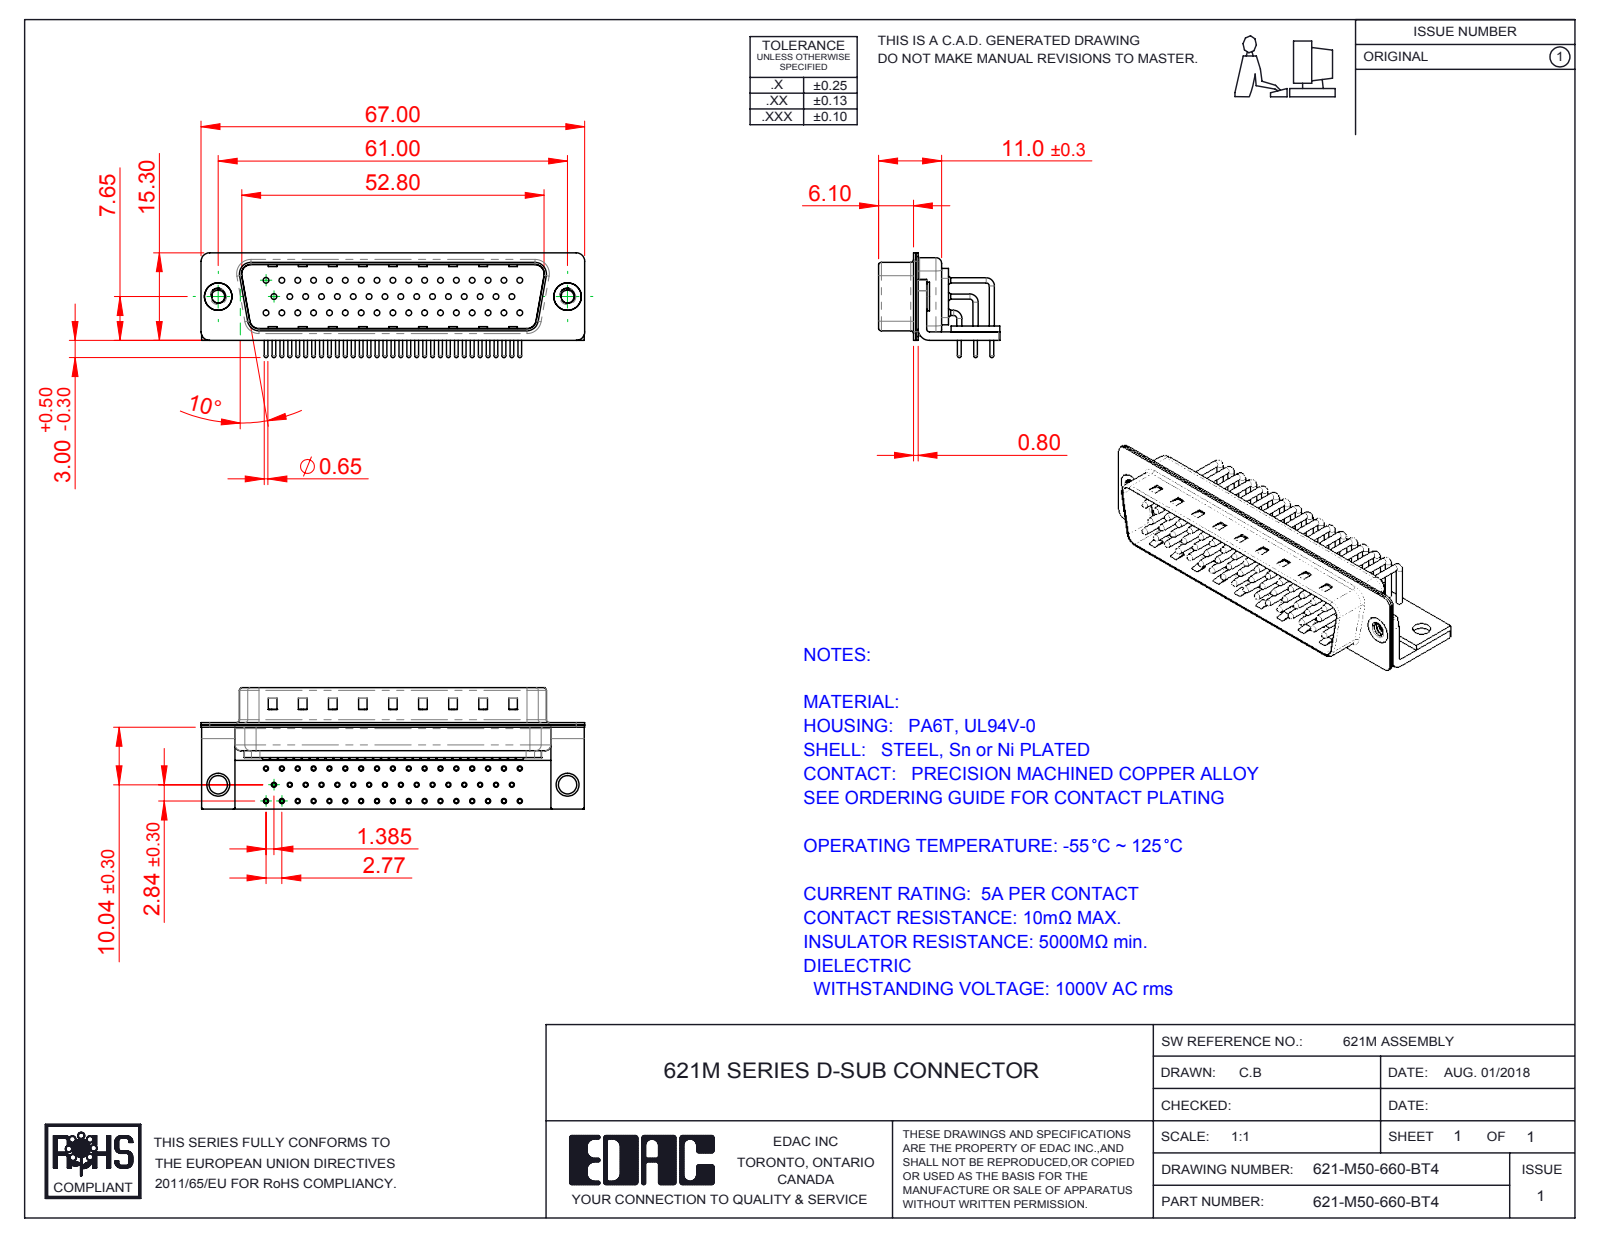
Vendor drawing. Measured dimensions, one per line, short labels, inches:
name: 621M Contact Row 3; 621M Housing_50 Contacts; 621M Stabilizer Bracket_50 Contacts; 621M Shell Front_50 Contacts (+6 more)
written by: SolidWorks 2016 (CONFIG_CONTROL_DESIGN)
unit: in
bodies: 58 solids, 6062 faces (3429 planar, 2063 cylindrical, 570 other)
size: 2.638 × 0.835 × 0.72
volume: 0.35 in³; area: 22.56 in²
holes: 50× ⌀0.035, 50× ⌀0.039, 50× ⌀0.067, 50× ⌀0.079, 2× ⌀0.089, 2× ⌀0.126, 2× ⌀0.157, 2× ⌀0.189
bosses: 58× ⌀0.035, 50× ⌀0.059, 50× ⌀0.026, 2× ⌀0.197, 2× ⌀0.193
rounds: 50× R0.04, 16× R0.01, 16× R0.059, 13× R0.079, 9× R0.02, 8× R0.063, 4× R0.024, 4× R0.026
face distances: 0.016, 0.039, 0.455, 0.033, 0.059, 0.224, 0.017, 0.47, 0.24, 0.461
hole spacings: 0.109, 0.124, 0.218, 0.327, 0.436, 0.545, 0.654, 0.763
